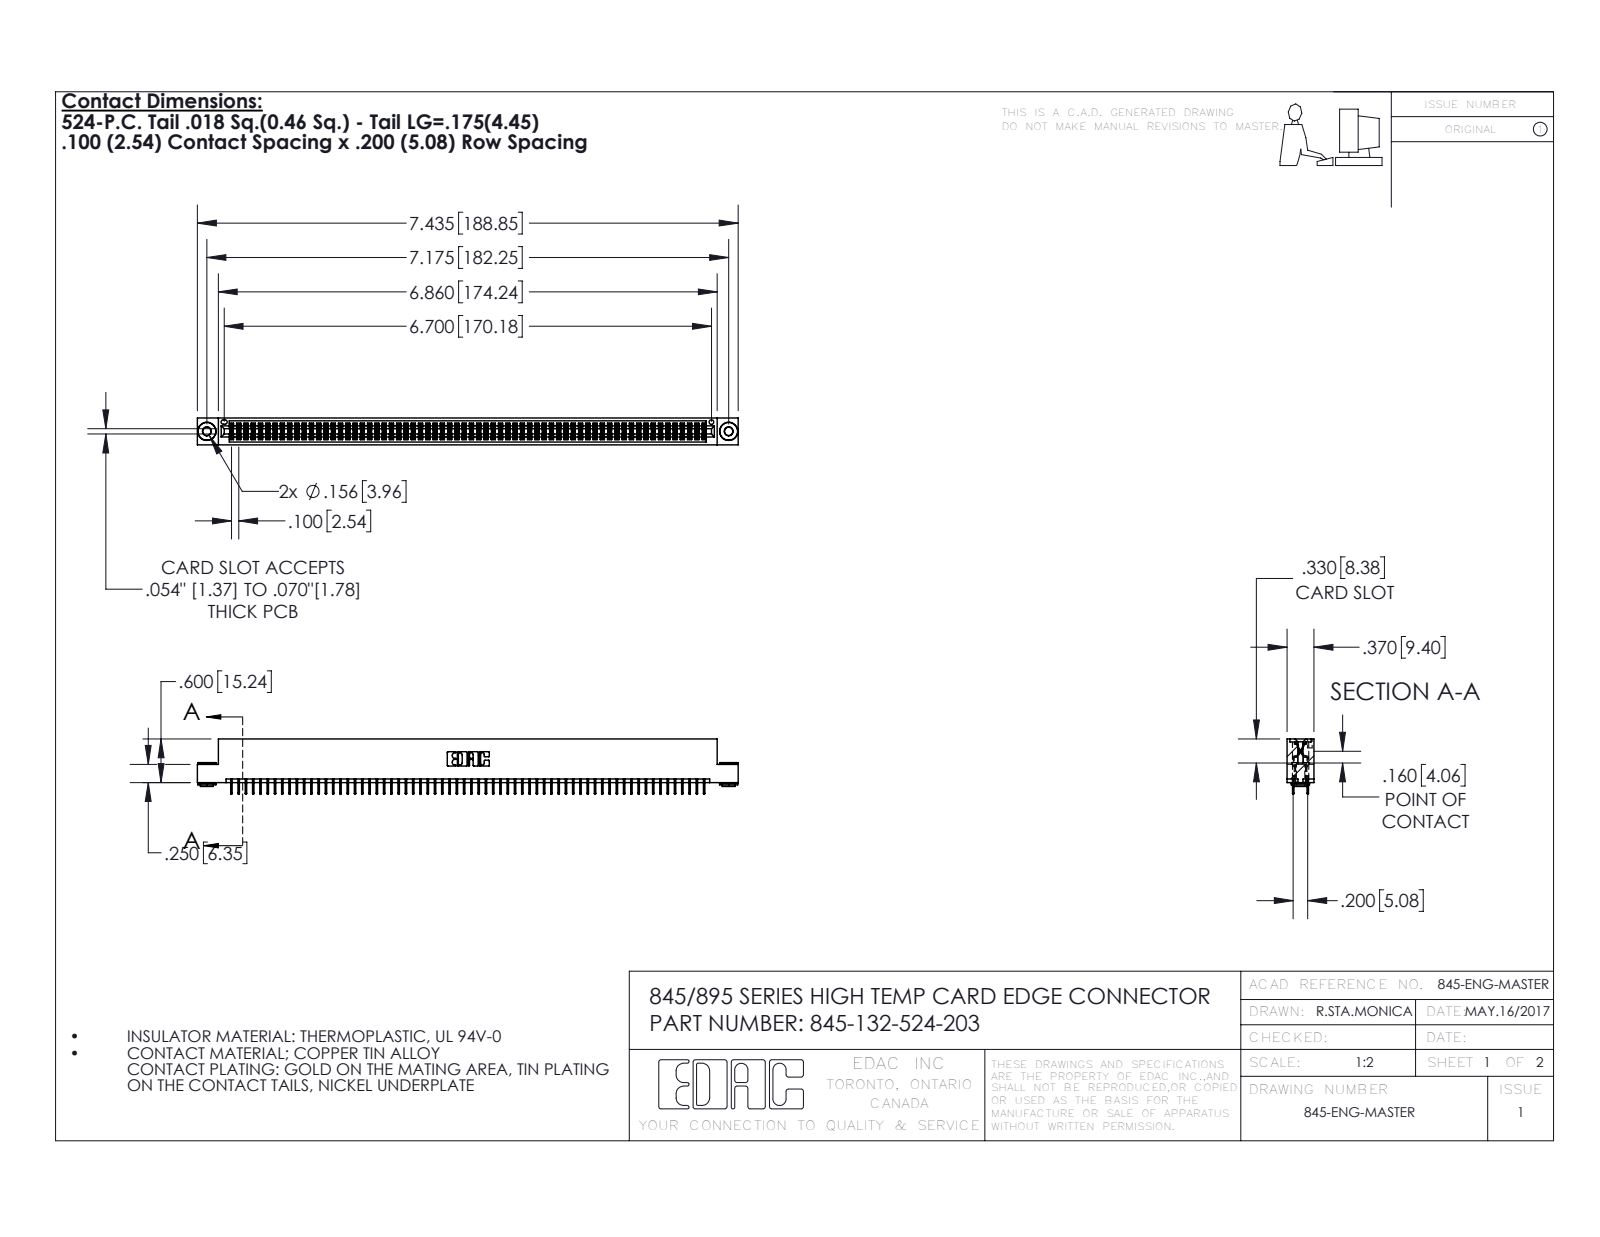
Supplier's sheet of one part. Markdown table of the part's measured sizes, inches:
| quantity | value |
| --- | --- |
| part name | 345-292-001_345-293-124; 345 Part_Flush Mounting Lugs - 0.156 Dia-TH; 345-250-002_345-250-002-102; 345-132-524-203 |
| STEP written by | SolidWorks 2016 (CONFIG_CONTROL_DESIGN) |
| units | inches |
| bodies | 135 solids, 7292 faces (5238 planar, 2046 cylindrical, 8 other) |
| overall size | 7.435 × 0.762 × 0.37 |
| volume | 1.122 in³ |
| surface area | 42.35 in² |
| round holes (diameter × count) | 0.116 × 2, 0.156 × 2, 0.064 × 1 |
| round bosses / shafts (diameter × count) | 0.25 × 2, 0.18 × 2, 0.136 × 2 |
| partial cylindrical surfaces (radius × count) | 0.006 × 198, 0.01 × 22, 0.007 × 6, 0.031 × 6, 0.026 × 3, 0.014 × 2, 0.019 × 2, 0.022 × 2 |
| main face-to-face distances | 0.072, 0.298, 0.2, 0.37, 0.025, 0.098, 0.272, 0.225, 0.072, 0.175 |
| hole center spacings | 0.27, 6.939, 7.175 |
